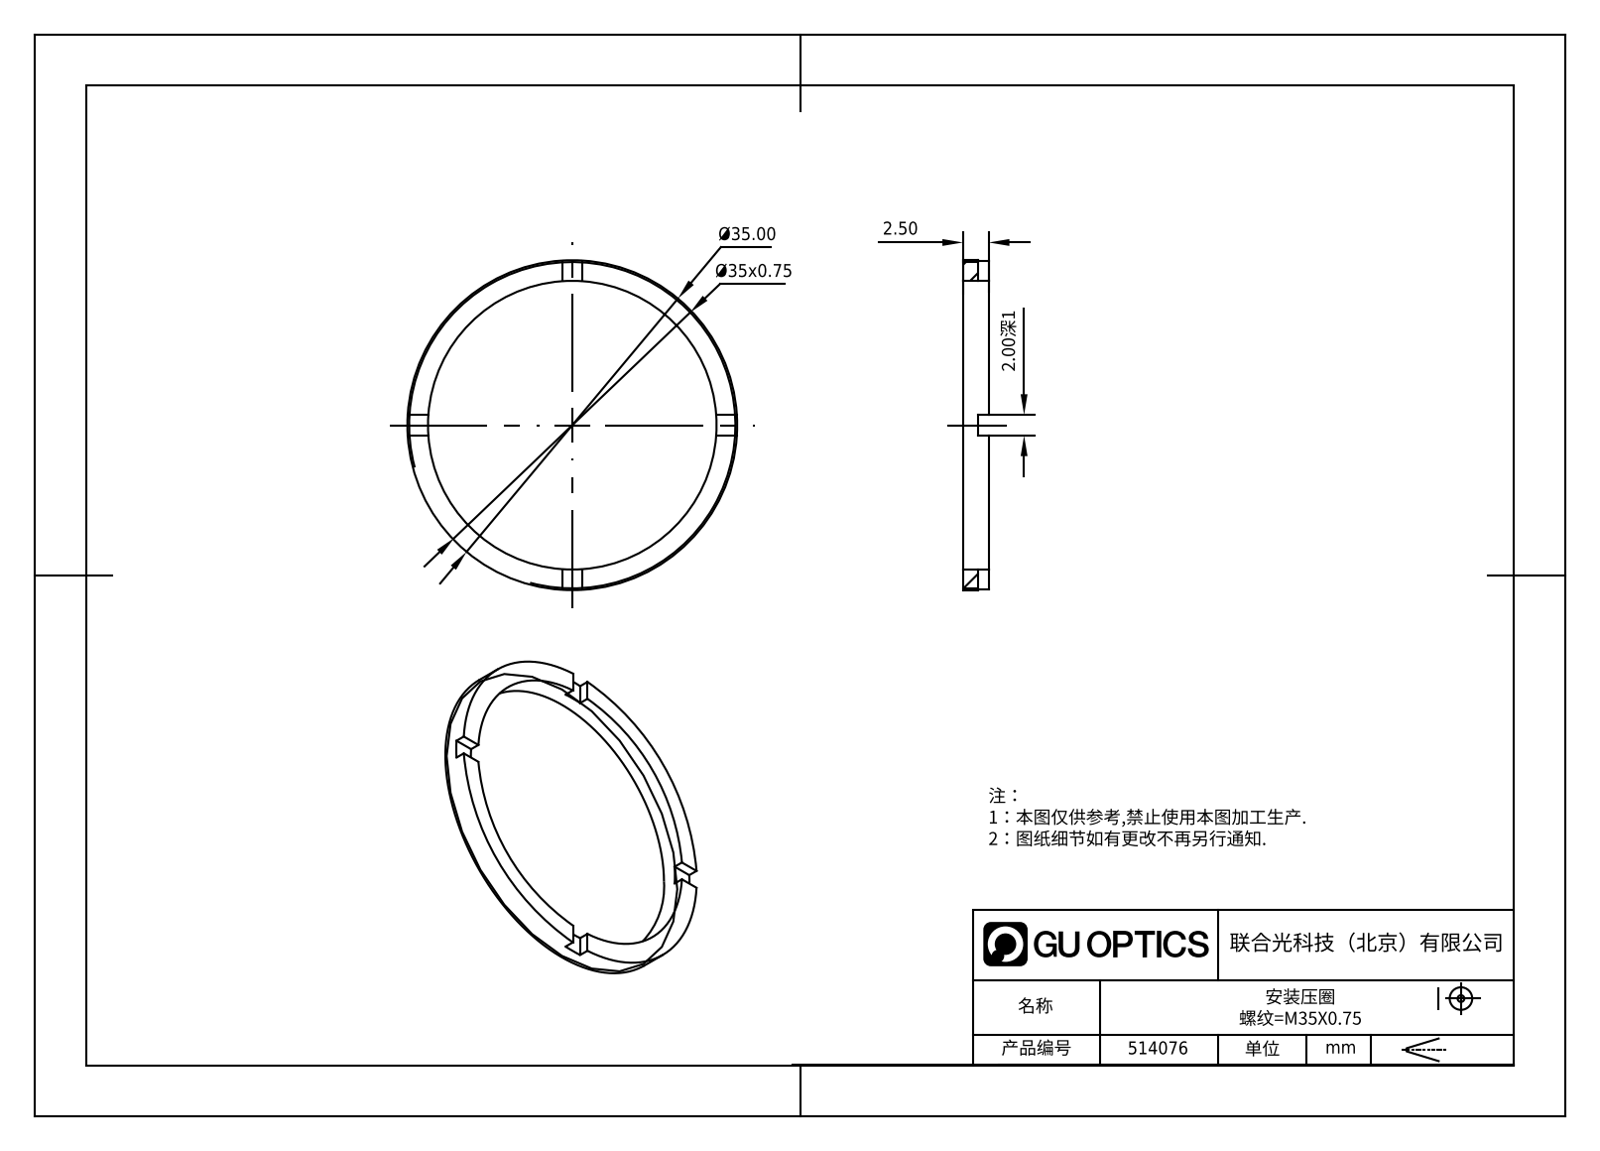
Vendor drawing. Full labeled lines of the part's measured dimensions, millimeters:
Part name (STEP PRODUCT): 514076
STEP written by: SolidWorks 2020 (CONFIG_CONTROL_DESIGN)
Units: millimetres
Bodies: 1 solid, 21 faces (17 planar, 4 cylindrical, 0 other)
Overall size (bounding box): 35 × 35 × 2.5
Volume: 502 mm³ · Surface area: 933 mm²
Round holes (diameter × count): ⌀31 ×1
Round bosses / shafts (diameter × count): ⌀35 ×1
Main face-to-face distances: 2.5, 1.5, 1, 2
